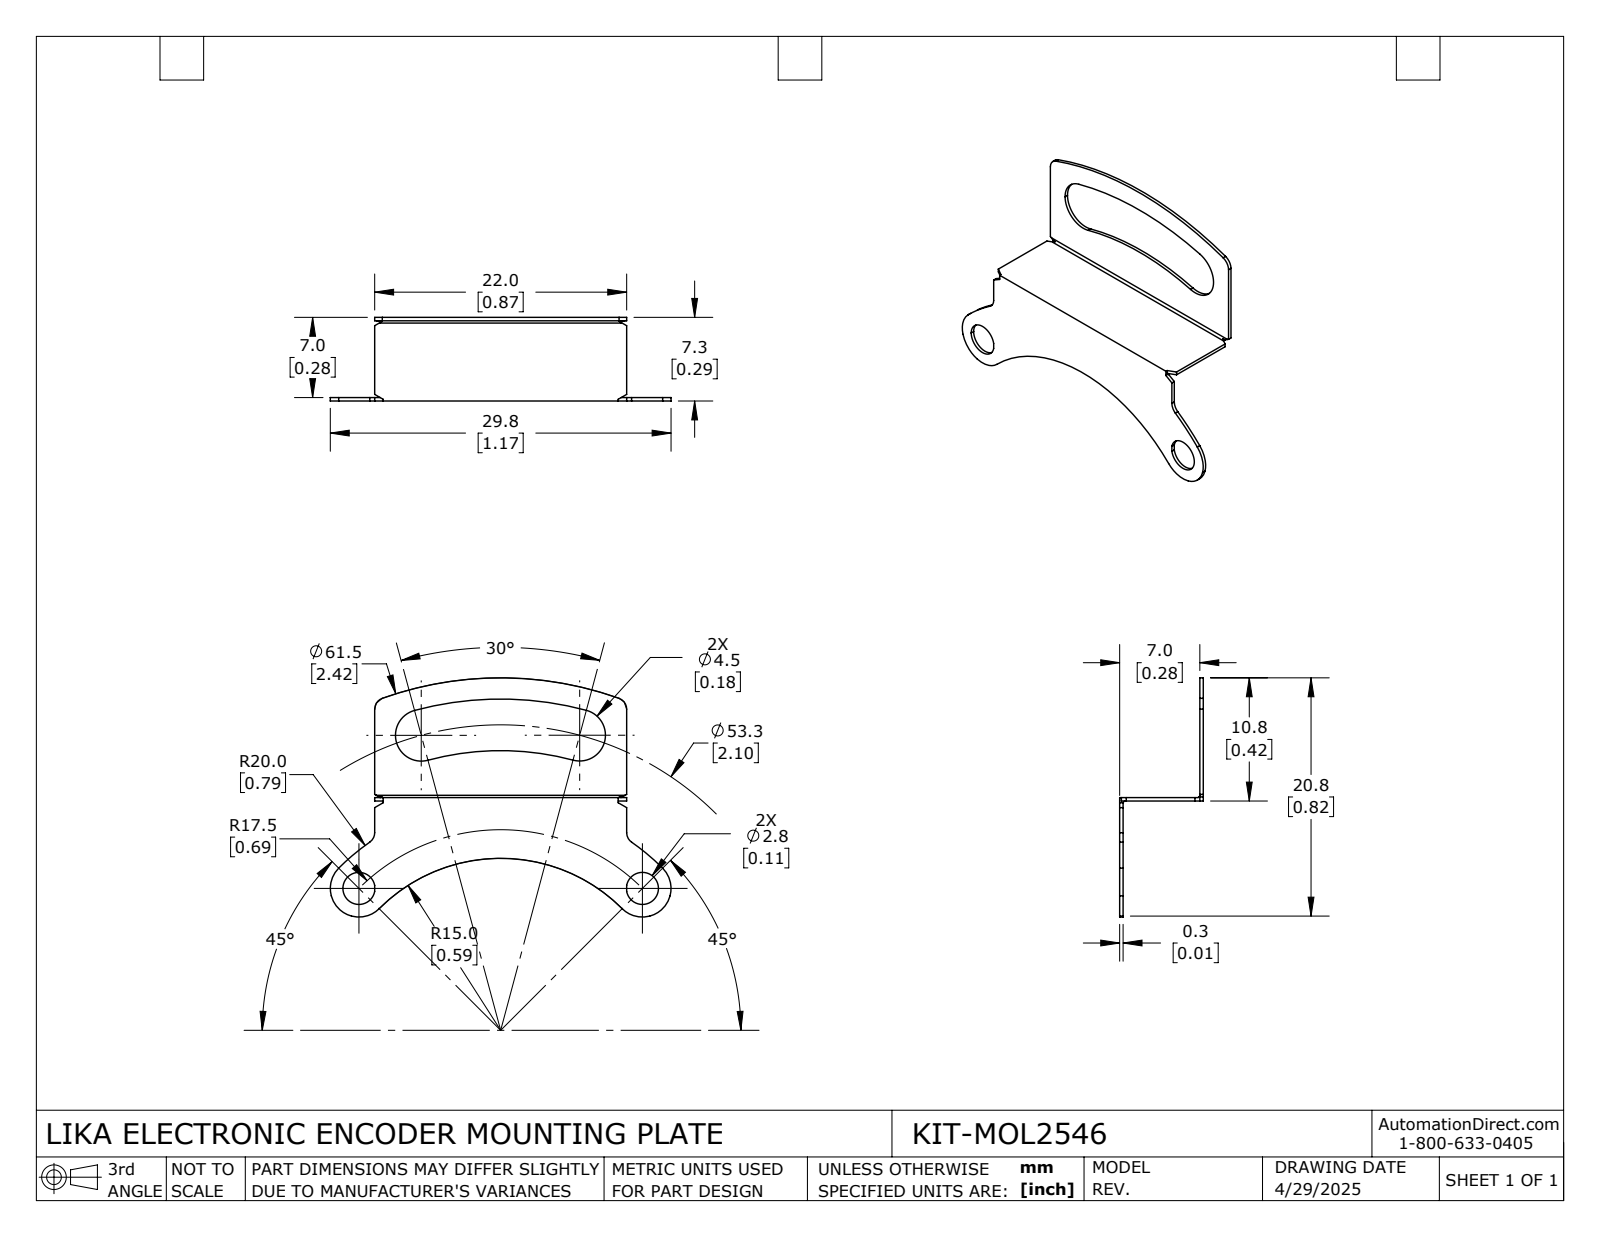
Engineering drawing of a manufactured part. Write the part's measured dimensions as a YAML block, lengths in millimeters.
part_name: "KIT-MOL2546"
step_written_by: "SolidWorks 2024 (AUTOMOTIVE_DESIGN)"
units: millimeters
bodies: {solids: 1, faces: 53, planar: 29, cylindrical: 6, other: 18}
overall_size: [29.7, 20.9, 7.3]
volume: 100
surface_area: 974
round_holes:
  - {diameter: 2.8, count: 2}
partial_cylinders:
  - {radius: 2.3, count: 2}
face_to_face_distances: [7, 7.3, 6.7, 22, 10, 0.7, 21.3, 16.2, 16.2, 0.4]
hole_center_spacings: [24.7]
